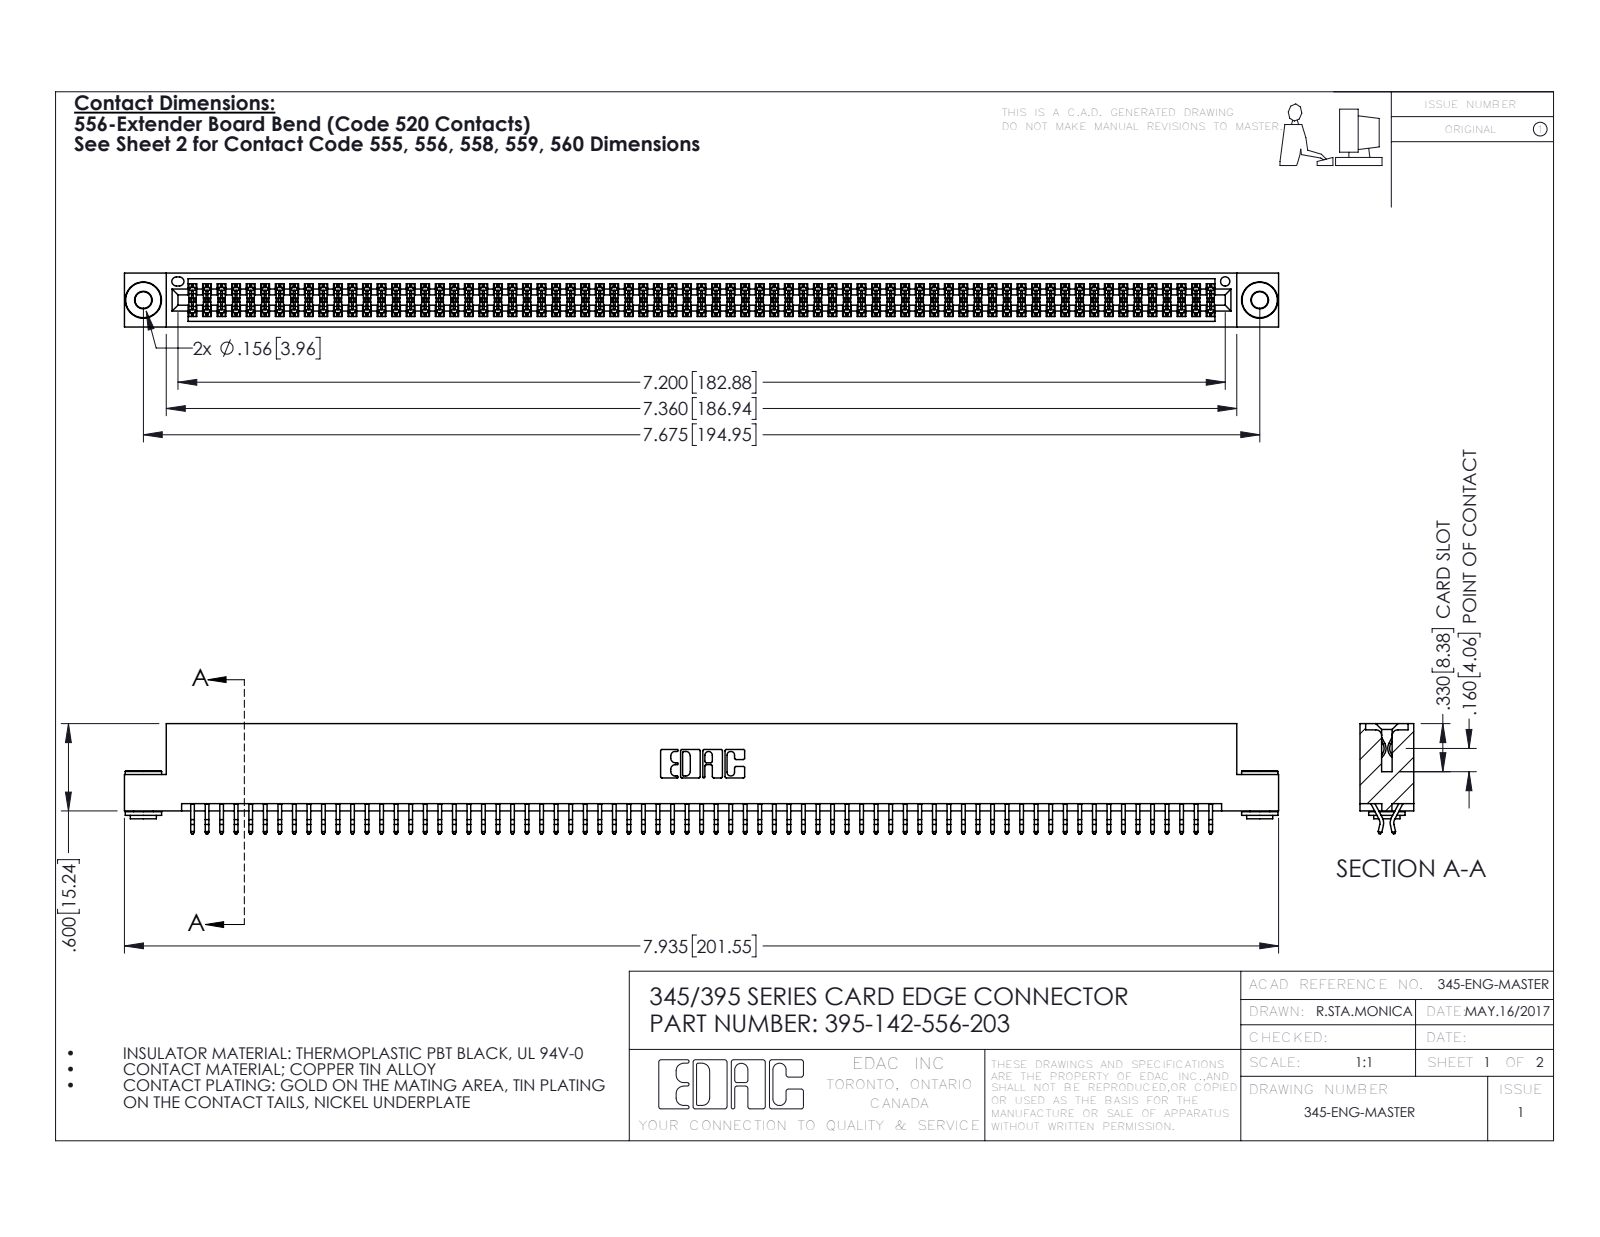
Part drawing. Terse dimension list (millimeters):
name: 345-292-001_556 Tail; 395-142-556-203; 345 Part_Flush Mounting Lugs - 0.156 Dia-TH; 345-250-002_345-250-002-102
written by: SolidWorks 2016 (CONFIG_CONTROL_DESIGN)
unit: mm
bodies: 145 solids, 8116 faces (5344 planar, 2764 cylindrical, 8 other)
size: 201.5 × 19.2 × 9.4
volume: 19 860 mm³; area: 30 000 mm²
holes: 2× ⌀2.9, 2× ⌀4, 1× ⌀1.6
bosses: 2× ⌀6.4, 2× ⌀4.6, 2× ⌀3.5
rounds: 213× R0.2, 22× R0.3, 6× R0.2, 6× R0.8, 3× R0.7, 2× R0.3, 2× R0.4, 2× R0.5
face distances: 1.8, 7.6, 9.4, 5.1, 0.6, 2.5, 6.9, 5.7, 4.4, 3.8
hole spacings: 6.9, 189, 194.9
